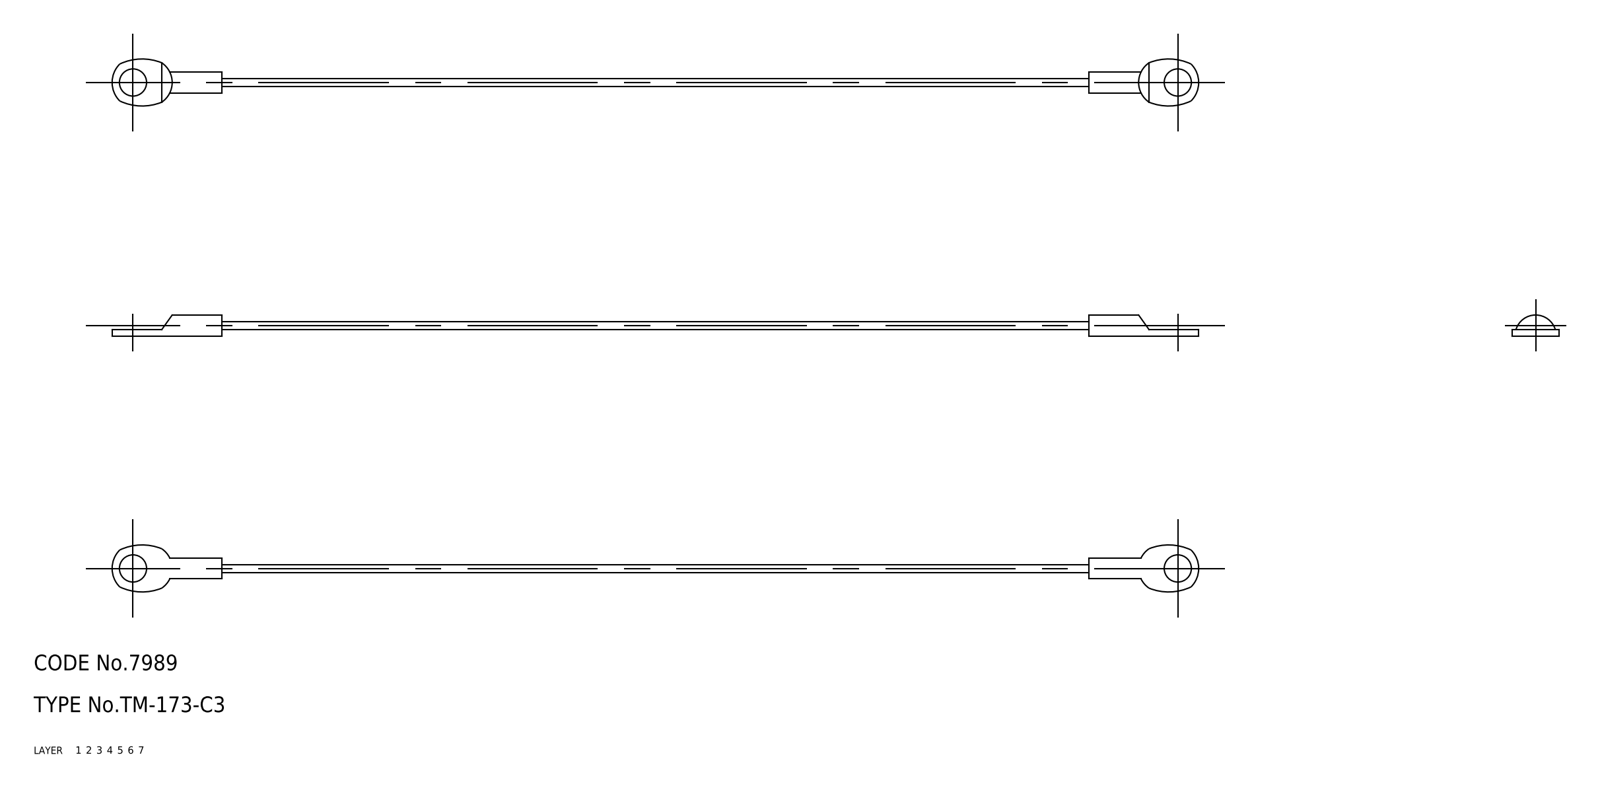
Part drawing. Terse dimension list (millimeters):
name: terminal; wire; TM_173_C3_28532_36
written by: CADfix (AUTOMOTIVE_DESIGN)
unit: mm
bodies: 3 solids, 56 faces (0 planar, 0 cylindrical, 56 other)
size: 208 × 9 × 4
volume: 708 mm³; area: 1 574 mm²
